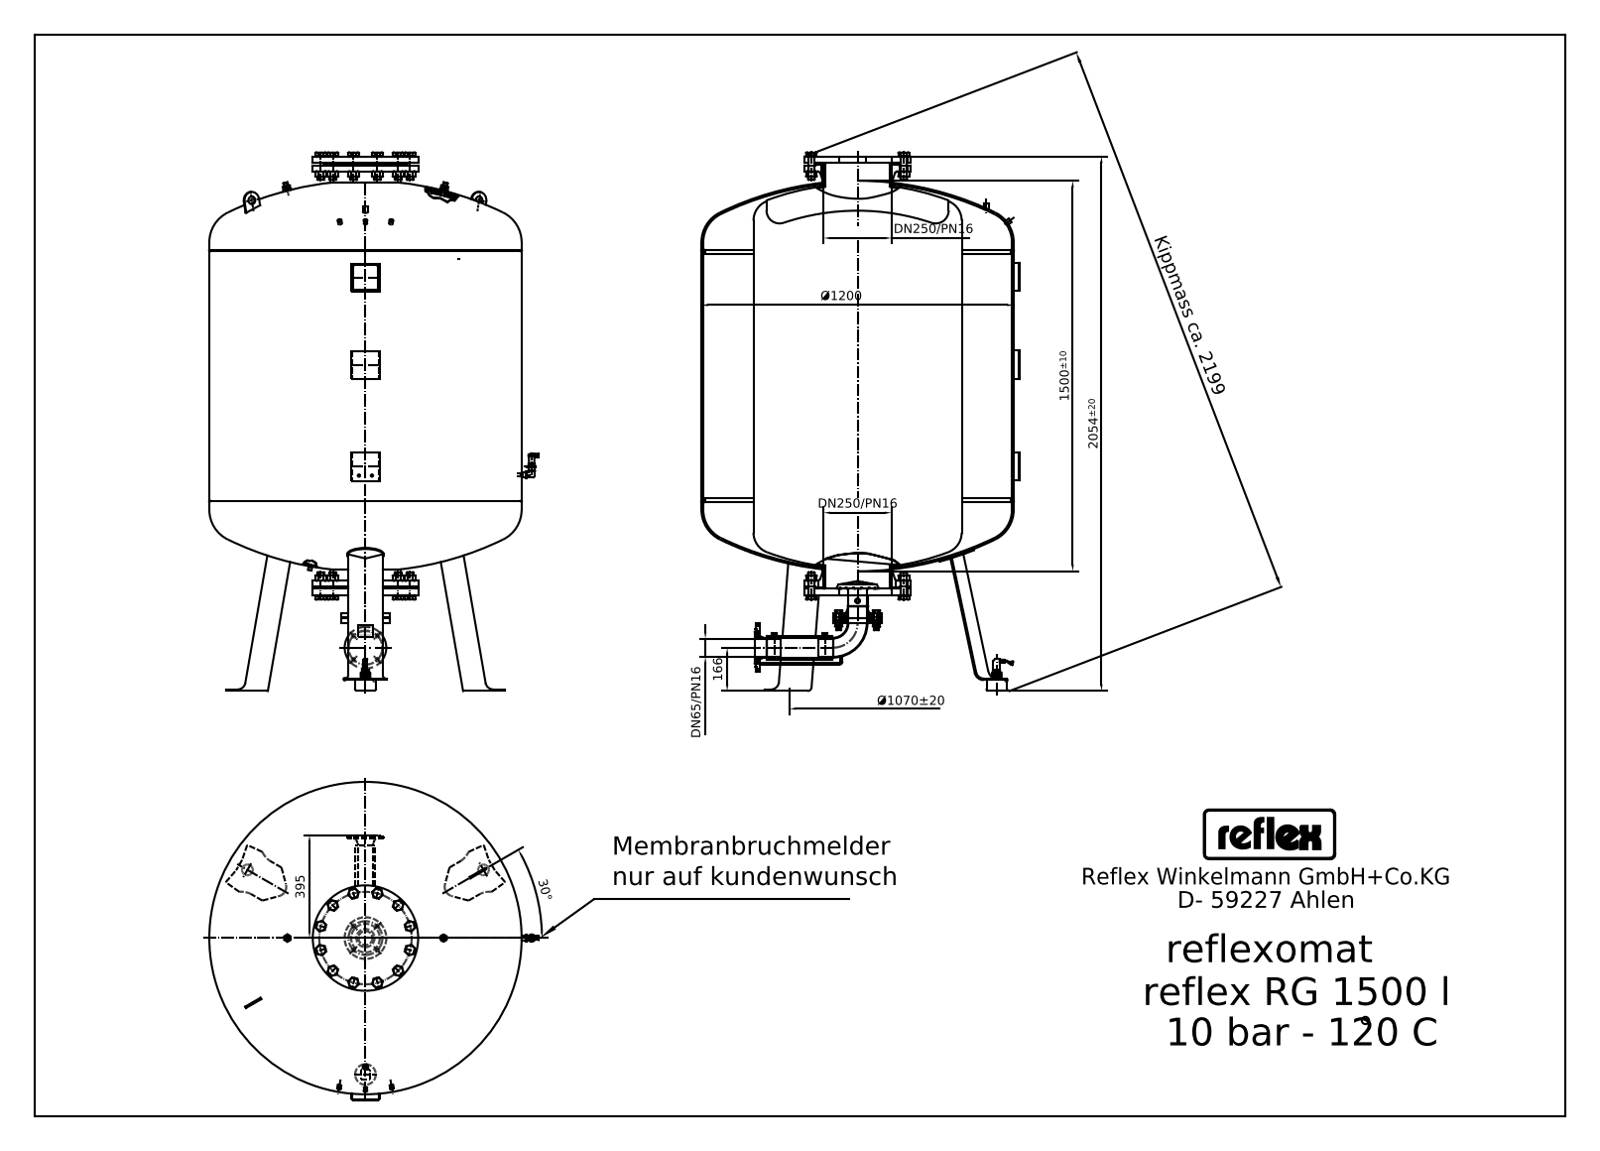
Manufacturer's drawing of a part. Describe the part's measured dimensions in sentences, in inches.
Its 3-D file was written by "Mechanical Desktop 2009 (CONFIG_CONTROL_DESIGN)". It is 33 solids with 1189 faces: 677 planar, 280 cylindrical and 232 other. Overall it measures 81.102 by 49.843 by 48.031 inches. Its volume is 93 920 cubic inches and its surface area 21 220 square inches. Round holes: 2 of diameter 0.354, 2 of diameter 0.451, 1 of diameter 0.138, 1 of diameter 0.315, 1 of diameter 0.589, 1 of diameter 1.181, 1 of diameter 10.252. Round bosses or shafts: 12 of diameter 0.63, 4 of diameter 0.472, 3 of diameter 0.839, 3 of diameter 0.728, 2 of diameter 2.996, 2 of diameter 1.102, 2 of diameter 0.787, 2 of diameter 0.394. Partial cylindrical surfaces (rounded edges, fillets, slot ends): 18 of radius 0.984, 10 of radius 0.079, 5 of radius 0.039, 4 of radius 0.332, 3 of radius 0.133, 3 of radius 0.236, 2 of radius 0.118, 2 of radius 0.227. The main face-to-face distances are 39.37, 0.866, 64.764, 1.063, 63.701, 13.189, 51.693, 12.323, 65.63, 52.559. The hole center spacings are 28.363, 1.969, 19.488, 24.39, 31.219, 46.141, 46.973, 73.224.
